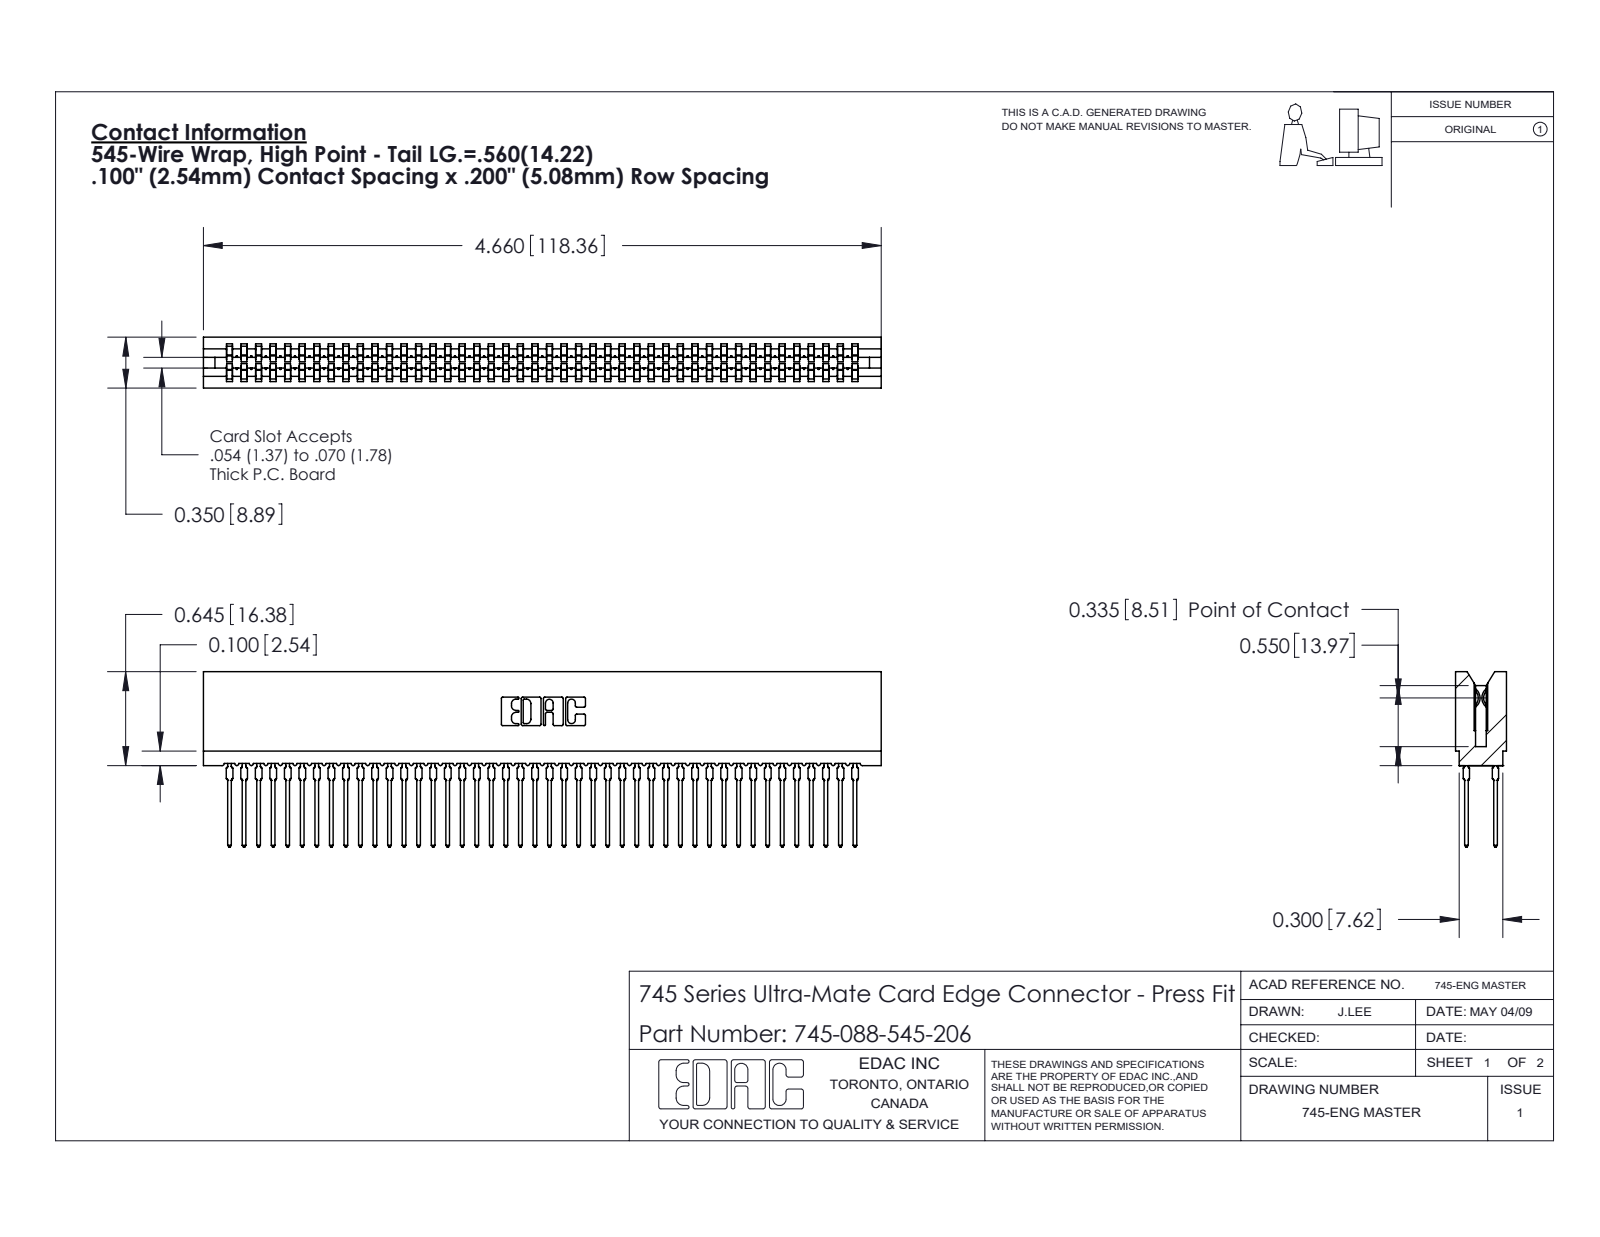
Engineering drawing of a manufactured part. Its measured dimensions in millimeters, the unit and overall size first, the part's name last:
Units: millimetres
Overall size (bounding box): 118.4 × 30.6 × 8.9
Partial cylindrical surfaces — rounded edges, fillets, slot ends (radius × count): R0.5 ×176, R0.4 ×88, R0.3 ×22, R0.1 ×8, R0.3 ×8, R0.2 ×6, R0.8 ×6, R0.7 ×3
Main face-to-face distances: 1.6, 7.3, 5.1, 8.9, 1.1, 7.7, 0.5, 6.2, 3.5, 5.4
Volume: 10 900 mm³ · Surface area: 23 650 mm²
Bodies: 89 solids, 7972 faces (4104 planar, 1580 cylindrical, 2288 other)
Part name (STEP PRODUCT): 745-088-545-206; 745-292-001_545; 745 Part_Insulator Option - 06
STEP written by: SolidWorks 2020 (CONFIG_CONTROL_DESIGN)
